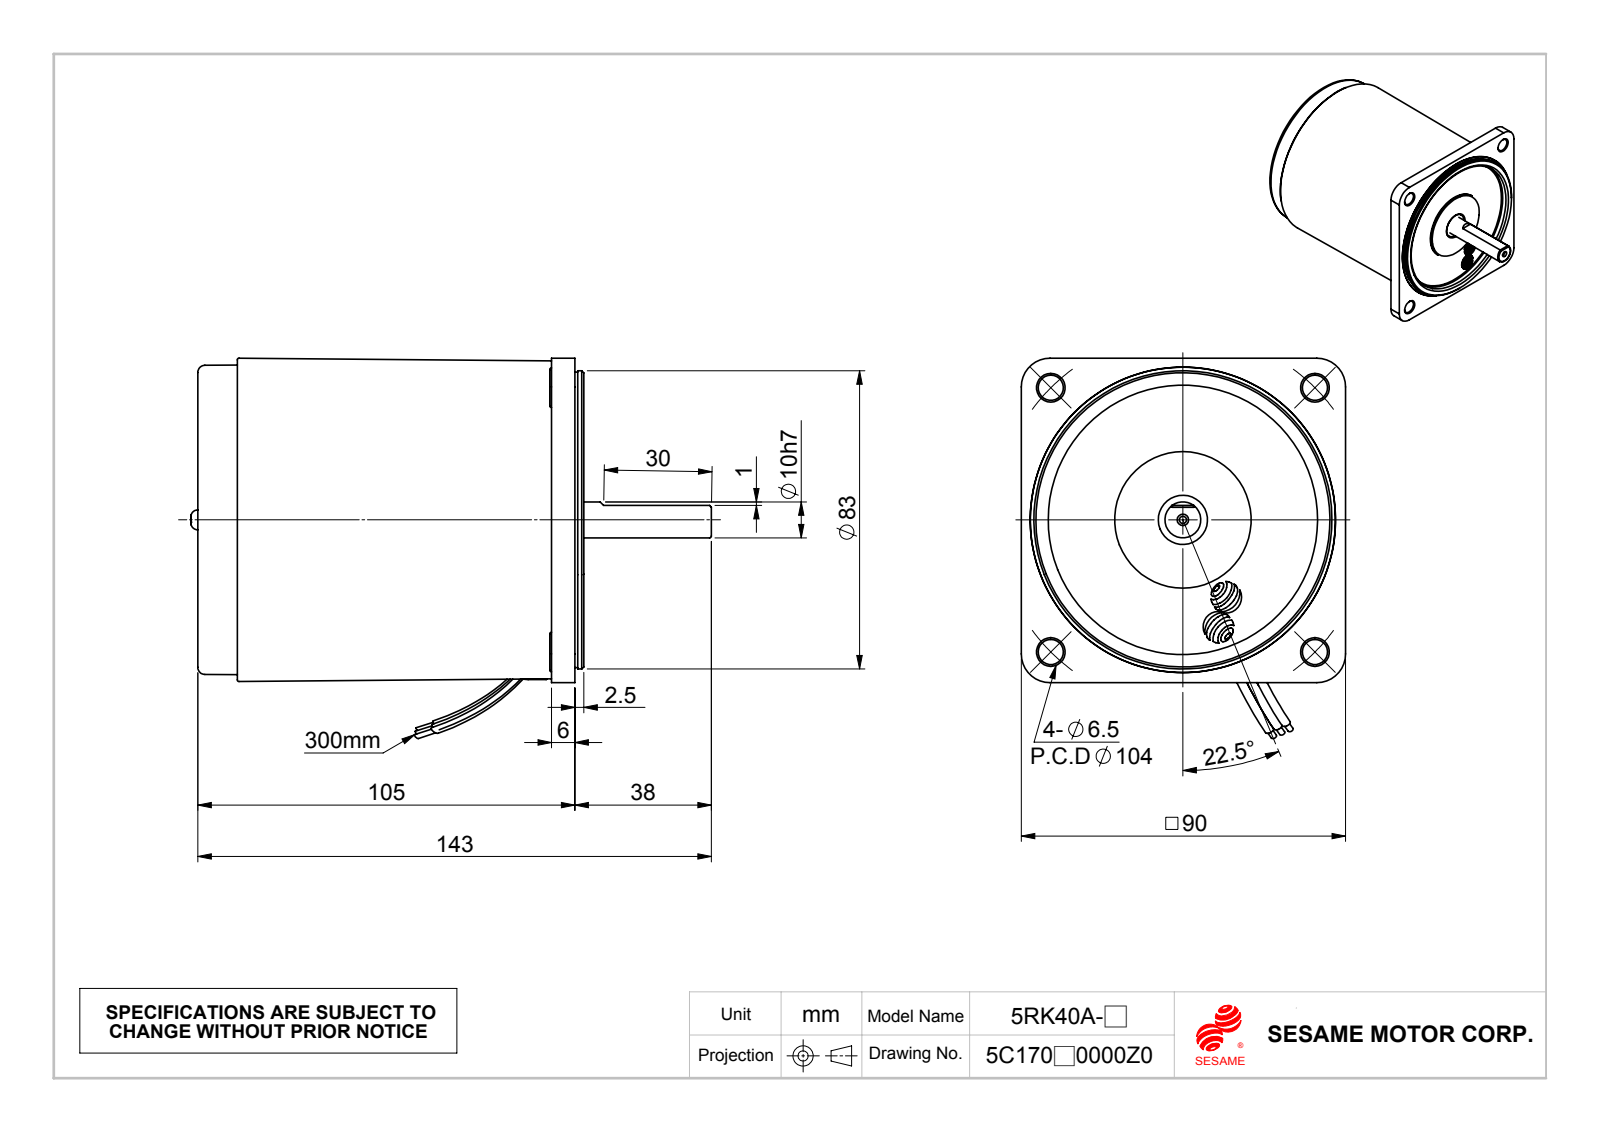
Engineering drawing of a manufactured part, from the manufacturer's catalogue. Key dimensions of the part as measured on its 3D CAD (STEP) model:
Part name (STEP PRODUCT): 40A; M540-RK; 線扣; 펥짰웰찿M5즤45x1t_Default
STEP written by: SolidWorks 2010 (CONFIG_CONTROL_DESIGN)
Units: millimetres
Bodies: 10 solids, 430 faces (107 planar, 217 cylindrical, 106 other)
Overall size (bounding box): 144.96 × 105.88 × 90.3
Volume: 667 256 mm³ · Surface area: 66 949 mm²
Round holes (diameter × count): ⌀7 ×4, ⌀2.5 ×3, ⌀4 ×2, ⌀2 ×1, ⌀7.2 ×1, ⌀9.5 ×1, ⌀13.7 ×1, ⌀26 ×1, ⌀58.1 ×1, ⌀75 ×1, ⌀85 ×1
Round bosses / shafts (diameter × count): ⌀5.5 ×2, ⌀3 ×2, ⌀84.22 ×1, ⌀83 ×1, ⌀82.2 ×1, ⌀45 ×1, ⌀38 ×1, ⌀10 ×1
Partial cylindrical surfaces — rounded edges, fillets, slot ends (radius × count): R0.25 ×8, R0.3 ×8, R0.78 ×8, R1.5 ×8, R1.66 ×8, R2.92 ×8, R0.2 ×4, R0.58 ×4
Main face-to-face distances: 1, 102.5, 0.9, 103.4, 101.5, 102.4, 103.5, 2.5, 1.5, 105
Hole centre spacings: 41.51, 52, 65.55, 73.54, 17.5, 104, 35
